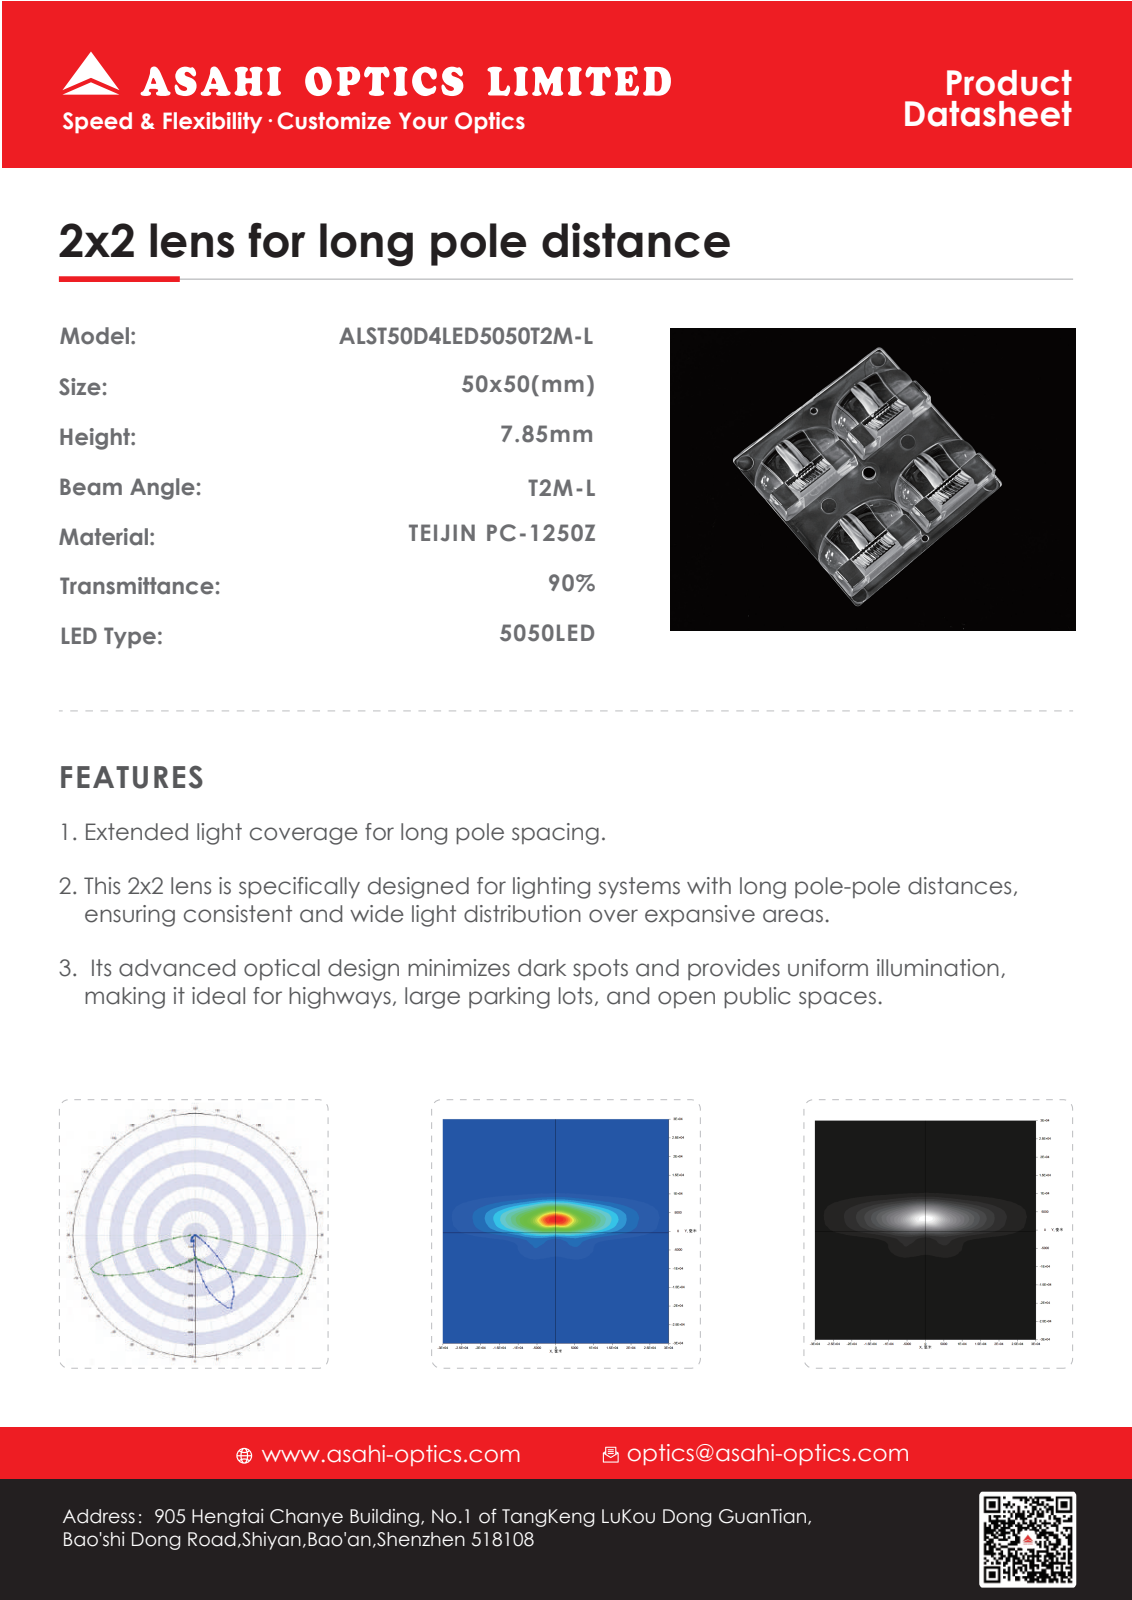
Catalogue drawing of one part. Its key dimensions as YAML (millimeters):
part_name: "1209-NEW"
step_written_by: "PRO/ENGINEER BY PARAMETRIC TECHNOLOGY CORPORATION, 2015240 (CONFIG_CONTROL_DESIGN)"
units: millimeters
bodies: {solids: 1, faces: 416, planar: 66, cylindrical: 48, other: 302}
overall_size: [50, 50, 10.75]
volume: 12225
surface_area: 8021
partial_cylinders:
  - {radius: 0.5, count: 34}
  - {radius: 1, count: 4}
face_to_face_distances: [2.25, 25.3, 1.59, 1, 1.25, 6.17, 23.71, 26.89, 5.61, 9.75]
